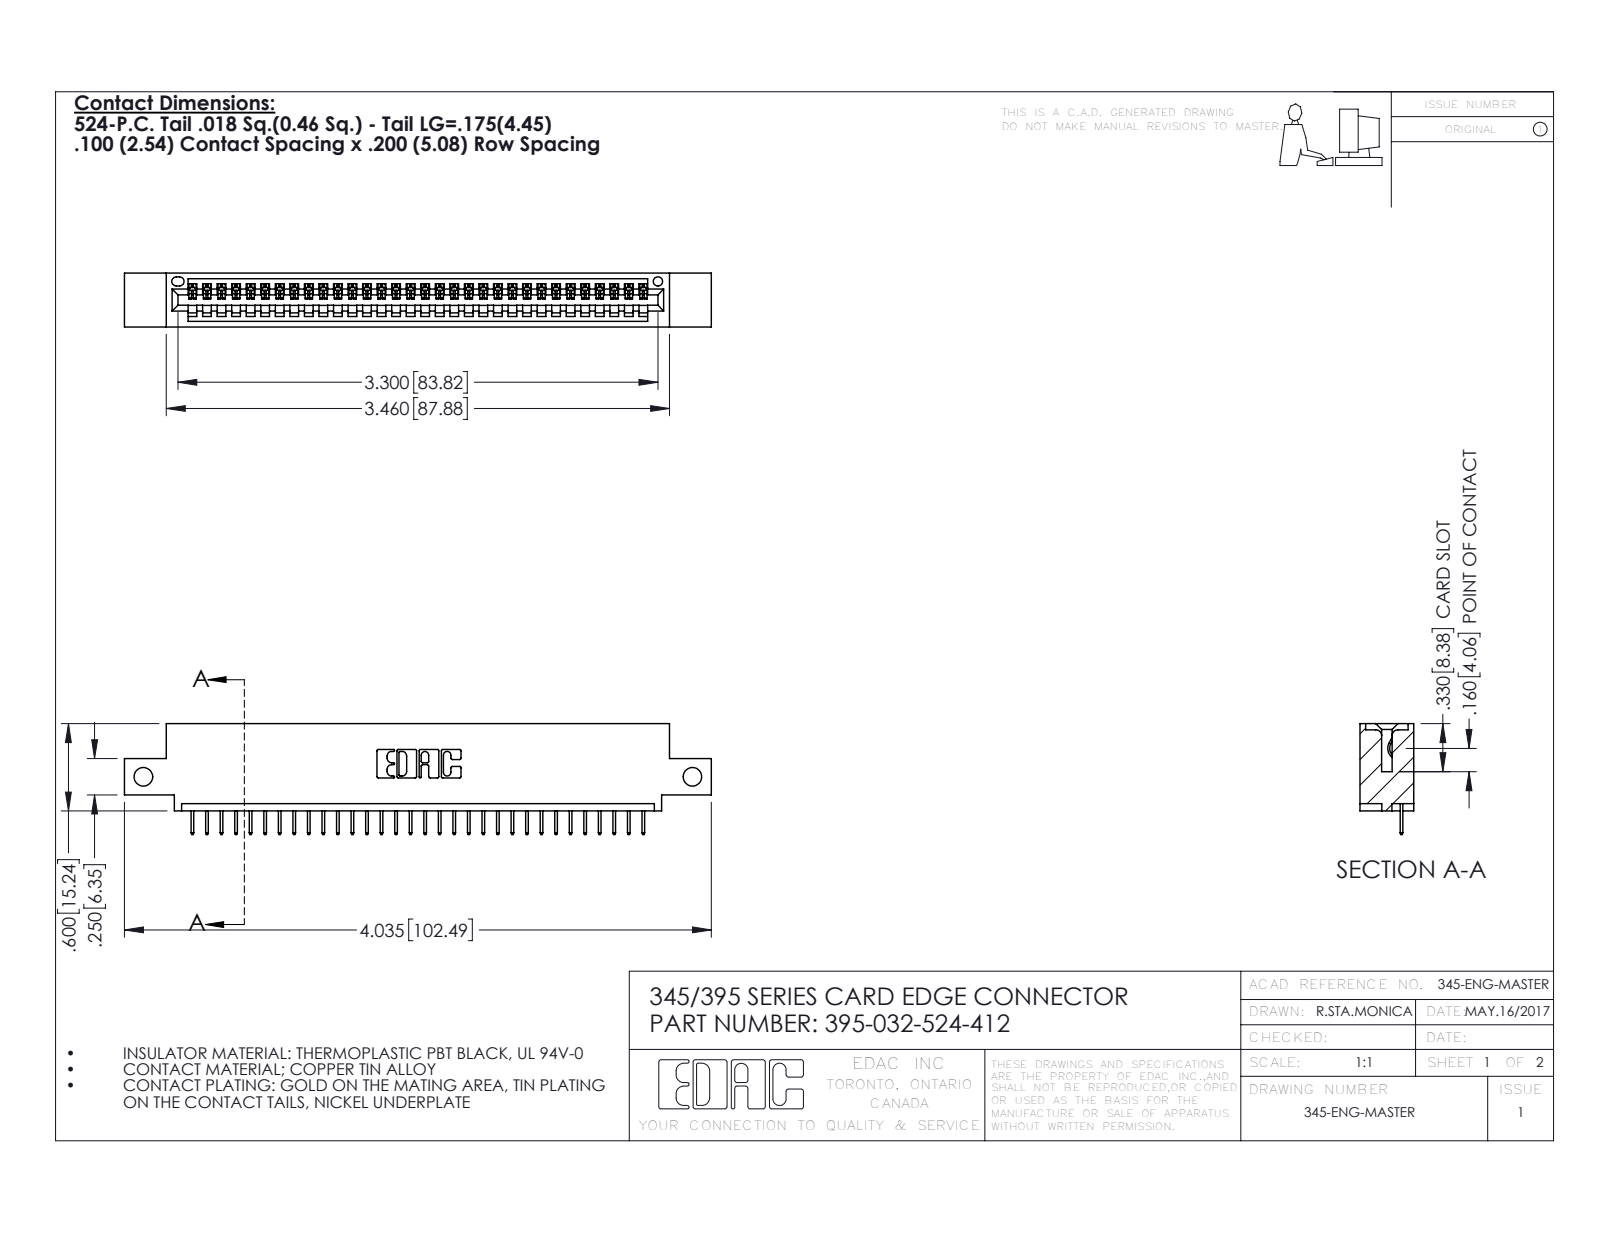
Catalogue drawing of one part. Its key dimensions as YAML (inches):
part_name: "395-032-524-412; 345 Part_0.110 Offset - Side Mount; 345-292-001_345-293-124"
step_written_by: "SolidWorks 2016 (CONFIG_CONTROL_DESIGN)"
units: inches
bodies: {solids: 33, faces: 2114, planar: 1556, cylindrical: 558, other: 0}
overall_size: [4.035, 0.762, 0.37]
volume: 0.572
surface_area: 18.36
round_holes:
  - {diameter: 0.128, count: 2}
  - {diameter: 0.064, count: 1}
partial_cylinders:
  - {radius: 0.006, count: 64}
  - {radius: 0.01, count: 22}
  - {radius: 0.007, count: 6}
  - {radius: 0.031, count: 6}
  - {radius: 0.026, count: 3}
  - {radius: 0.031, count: 2}
  - {radius: 0.04, count: 2}
  - {radius: 0.014, count: 1}
face_to_face_distances: [0.072, 0.298, 0.37, 0.2, 0.098, 0.272, 0.025, 0.225, 0.072, 0.149]
hole_center_spacings: [3.775]
